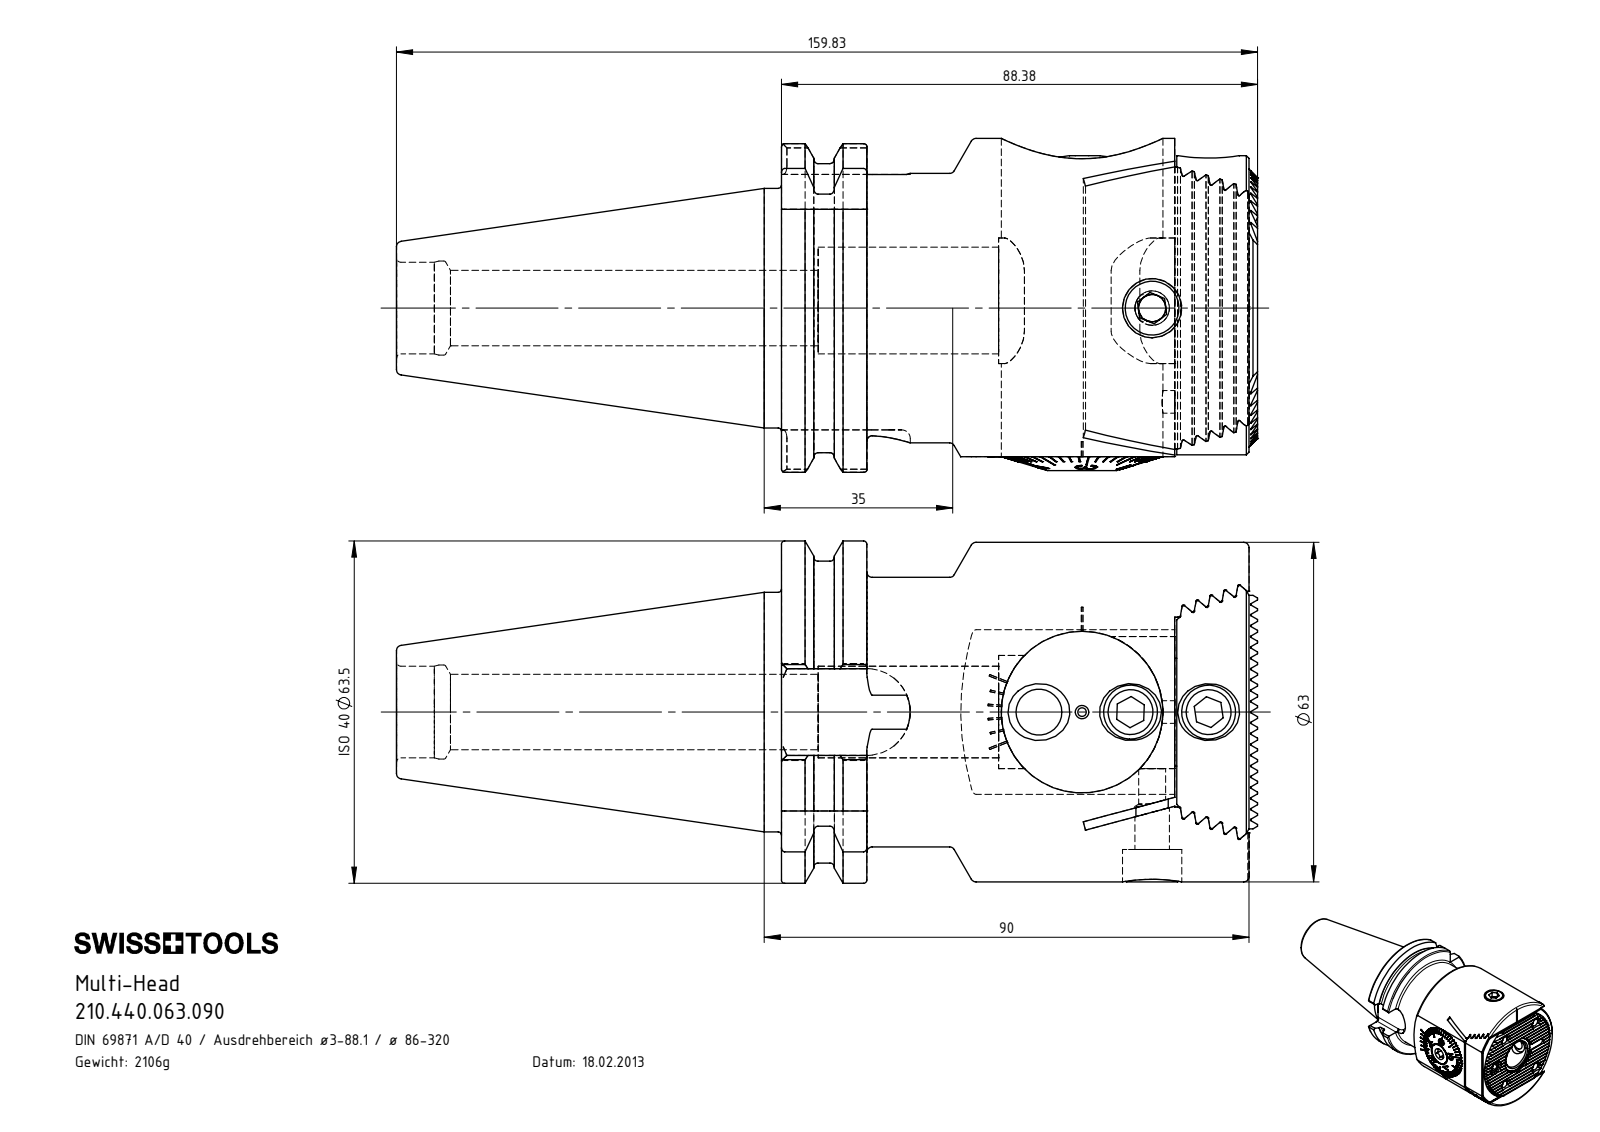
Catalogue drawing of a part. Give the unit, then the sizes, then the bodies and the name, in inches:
Units: inches
Overall size (bounding box): 6.293 × 2.5 × 2.439
Round holes (diameter × count): ⌀0.165 ×5, ⌀0.335 ×4, ⌀0.268 ×3, ⌀0.433 ×3, ⌀0.551 ×2, ⌀0.787 ×2, ⌀0.039 ×1, ⌀0.063 ×1, ⌀0.13 ×1, ⌀0.197 ×1, ⌀0.252 ×1, ⌀0.315 ×1
Round bosses / shafts (diameter × count): ⌀0.394 ×3, ⌀2.48 ×1, ⌀1.969 ×1, ⌀1.75 ×1, ⌀1.181 ×1, ⌀1.18 ×1, ⌀1.177 ×1, ⌀0.984 ×1
Partial cylindrical surfaces — rounded edges, fillets, slot ends (radius × count): R0.006 ×21, R0.008 ×20, R0.063 ×8, R0.236 ×6, R0.157 ×2, R1.22 ×2, R0.079 ×1, R0.276 ×1
Main face-to-face distances: 0.094, 0.016, 0.068, 2.874, 2.89, 0.281, 0.188, 0.187, 0.341, 0.205
Hole centre spacings: 0.659, 0.71, 0.808, 0.945, 1.181, 1.37, 1.513, 0.287
Volume: 16.37 in³ · Surface area: 115.1 in²
Bodies: 14 solids, 1118 faces (556 planar, 253 cylindrical, 309 other)
Part name (STEP PRODUCT): MH1-BG2.001.056_D; MH1-BG1.001.049; A55-BG1.012.007_B; MH1-BG1.001.049_B (+8 more)
STEP written by: SolidWorks 2017 (CONFIG_CONTROL_DESIGN)
